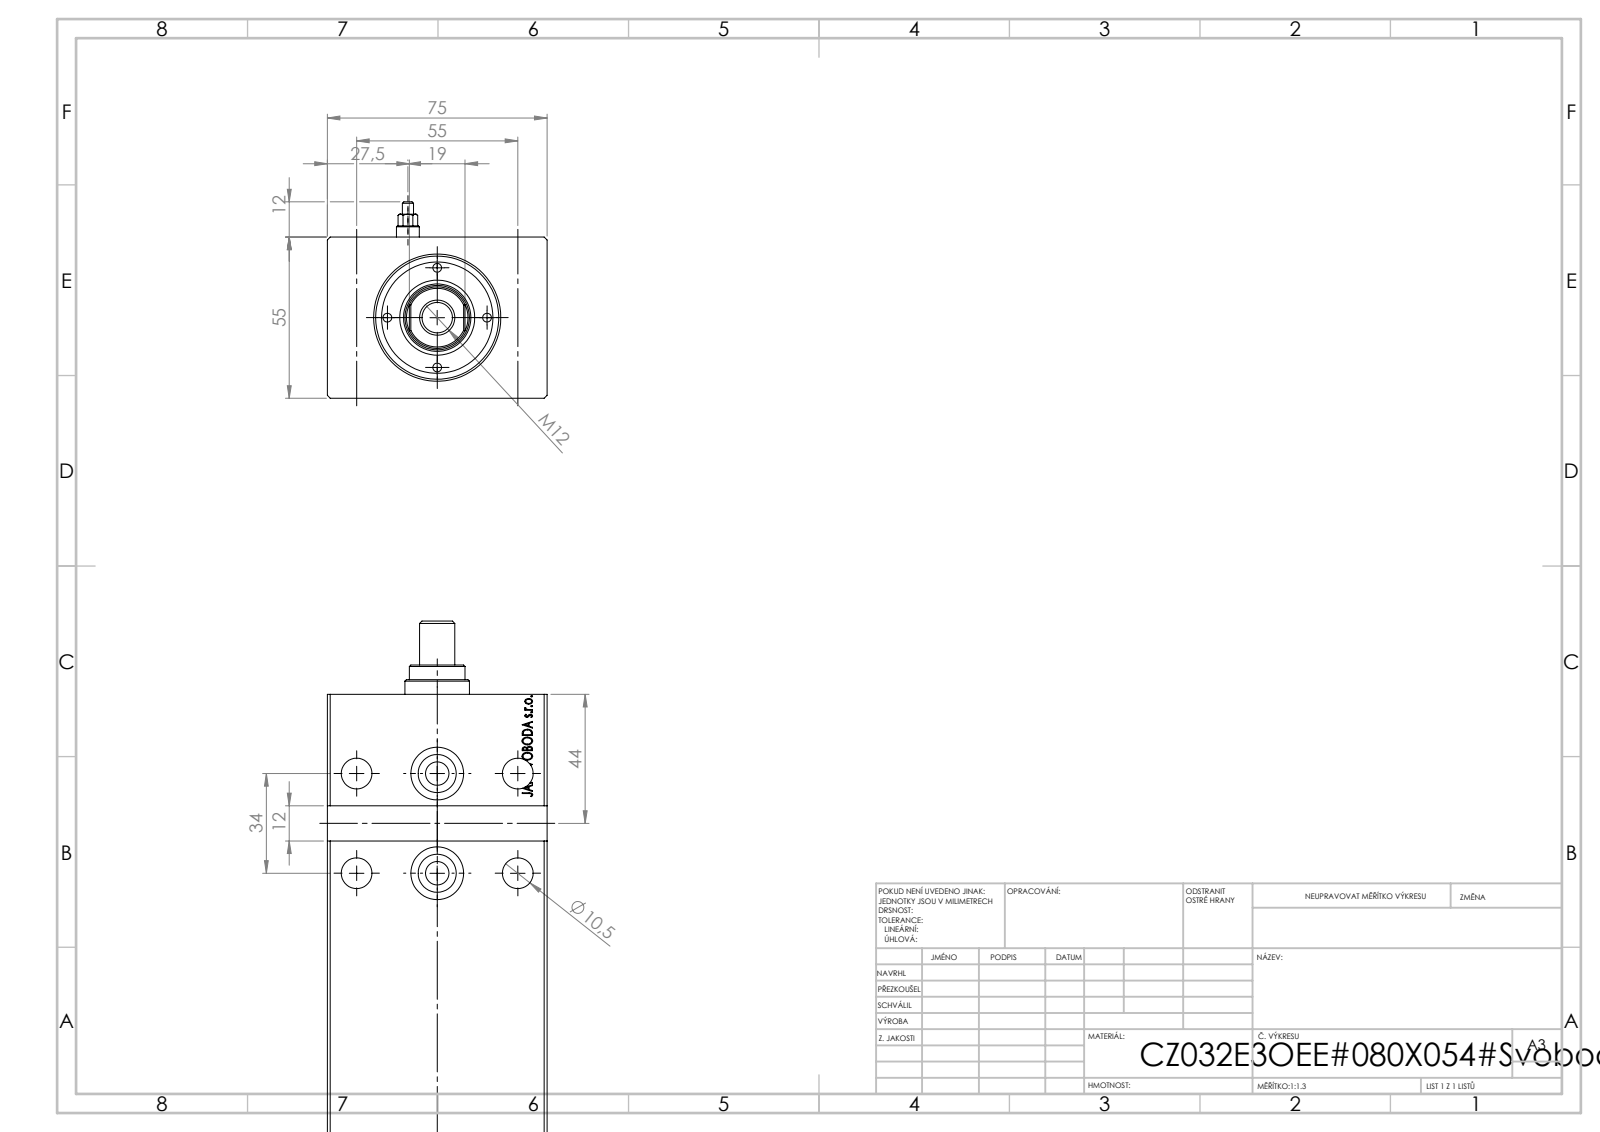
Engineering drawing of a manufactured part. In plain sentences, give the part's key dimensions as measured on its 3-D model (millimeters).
The part is named "V500CZ_B_VC; Zatka_Cushioning3; V500CZ_VCP_E; V500CZ_SMALL_MALE_METRIC (+1 more)". Its 3-D file was written by "SolidWorks 2019 (CONFIG_CONTROL_DESIGN)". It is 6 solids with 862 faces: 402 planar, 68 cylindrical and 392 other. Overall it measures 200 by 75 by 67 millimeters. Its volume is 668 295 cubic millimeters and its surface area 99 446 square millimeters. Round holes: 5 of diameter 10.5, 4 of diameter 3, 4 of diameter 8, 2 of diameter 1.8, 2 of diameter 18, 1 of diameter 22, 1 of diameter 23, 1 of diameter 32, 1 of diameter 36, 1 of diameter 42. Round bosses or shafts: 2 of diameter 13, 2 of diameter 7.8, 2 of diameter 3.8, 1 of diameter 38, 1 of diameter 12. Partial cylindrical surfaces (rounded edges, fillets, slot ends): 1 of radius 10.5. The main face-to-face distances are 55, 75, 175, 10, 161.2, 13.8, 151.2, 165, 174.8, 164.8. The hole center spacings are 34, 17, 24.04, 27.5, 43.73, 55, 64.66, 11.66.
